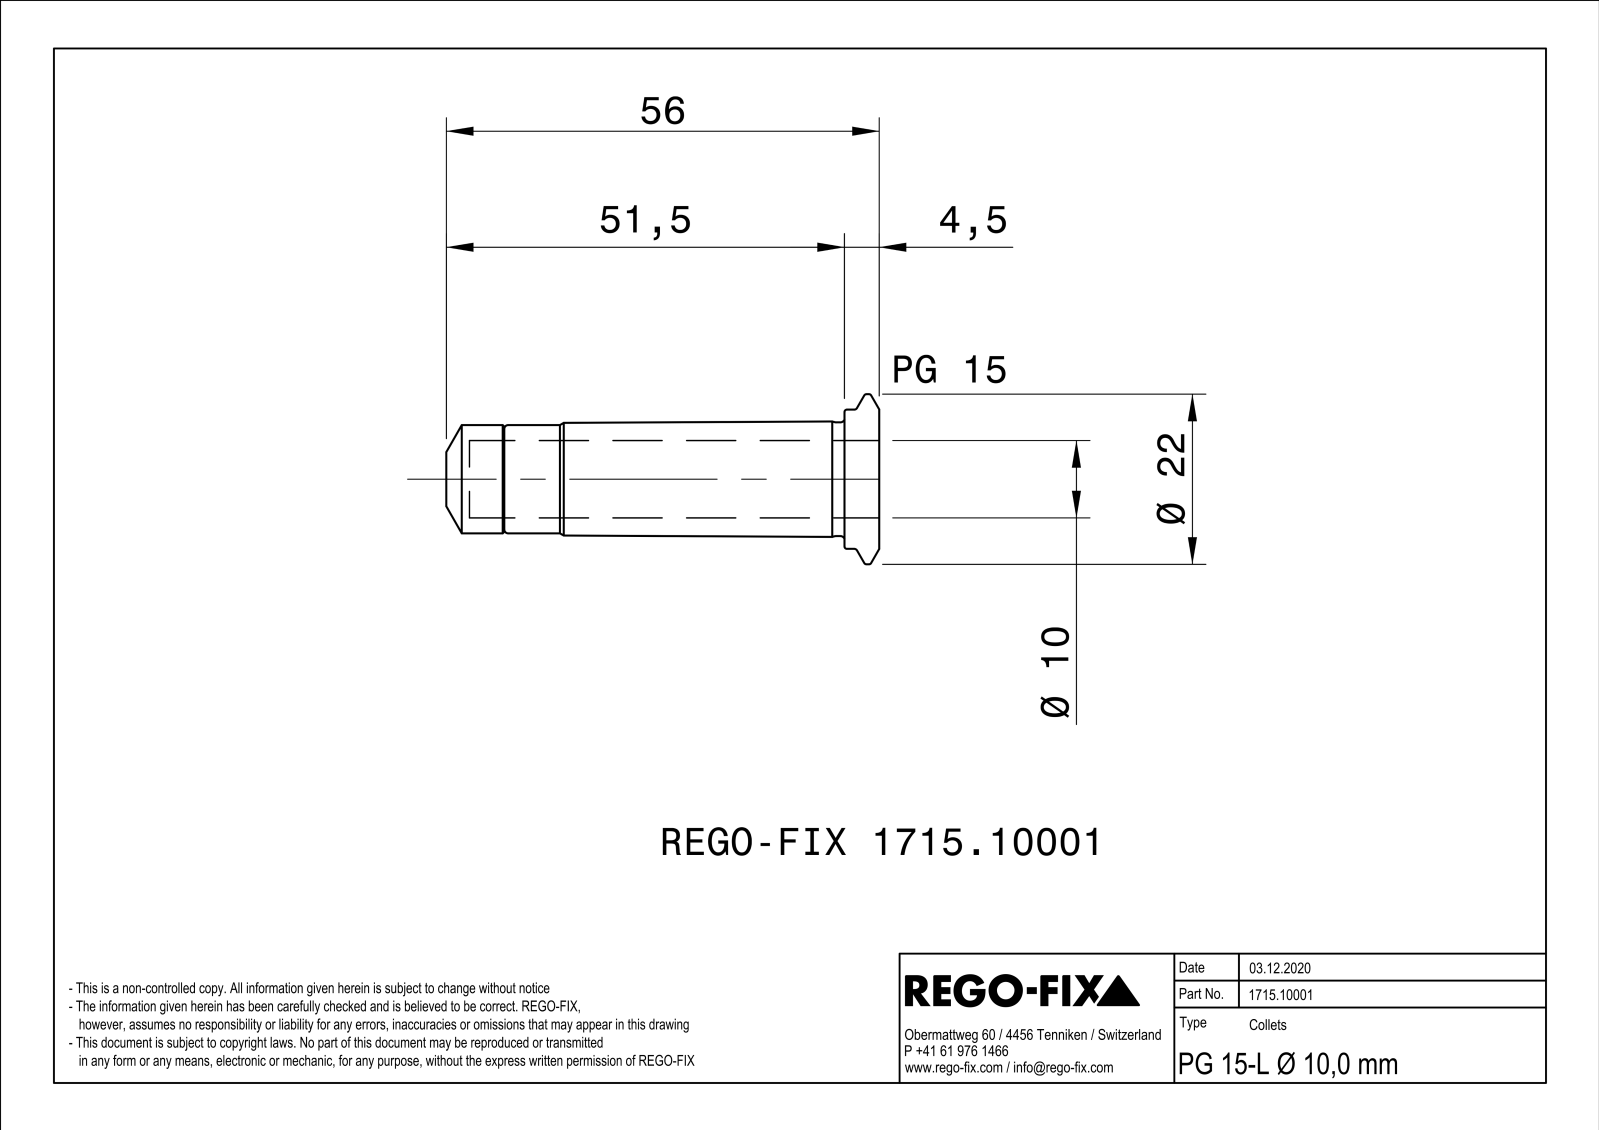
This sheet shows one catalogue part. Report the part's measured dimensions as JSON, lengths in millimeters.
{"part_name": "0016446", "step_written_by": "SIEMENS PLM Software Solid Edge ST10 (AUTOMOTIVE_DESIGN)", "units": "millimeters", "bodies": {"solids": 1, "faces": 94, "planar": 26, "cylindrical": 28, "other": 40}, "overall_size": [56, 22, 21.99], "volume_mm3": 658, "surface_area_mm2": 5763, "round_holes": [[5.5, 1], [10, 1], [10.2, 1], [12.2, 1]], "round_bosses_or_shafts": [[22, 1], [18, 1], [14.7, 1], [14, 1], [12, 1], [11.7, 1]], "partial_cylinders_radius": [[0.5, 6], [2, 3]], "face_to_face_distances": [1, 48.5, 4.5, 44, 1.5, 56, 51.5, 7.5, 41.5, 37]}
